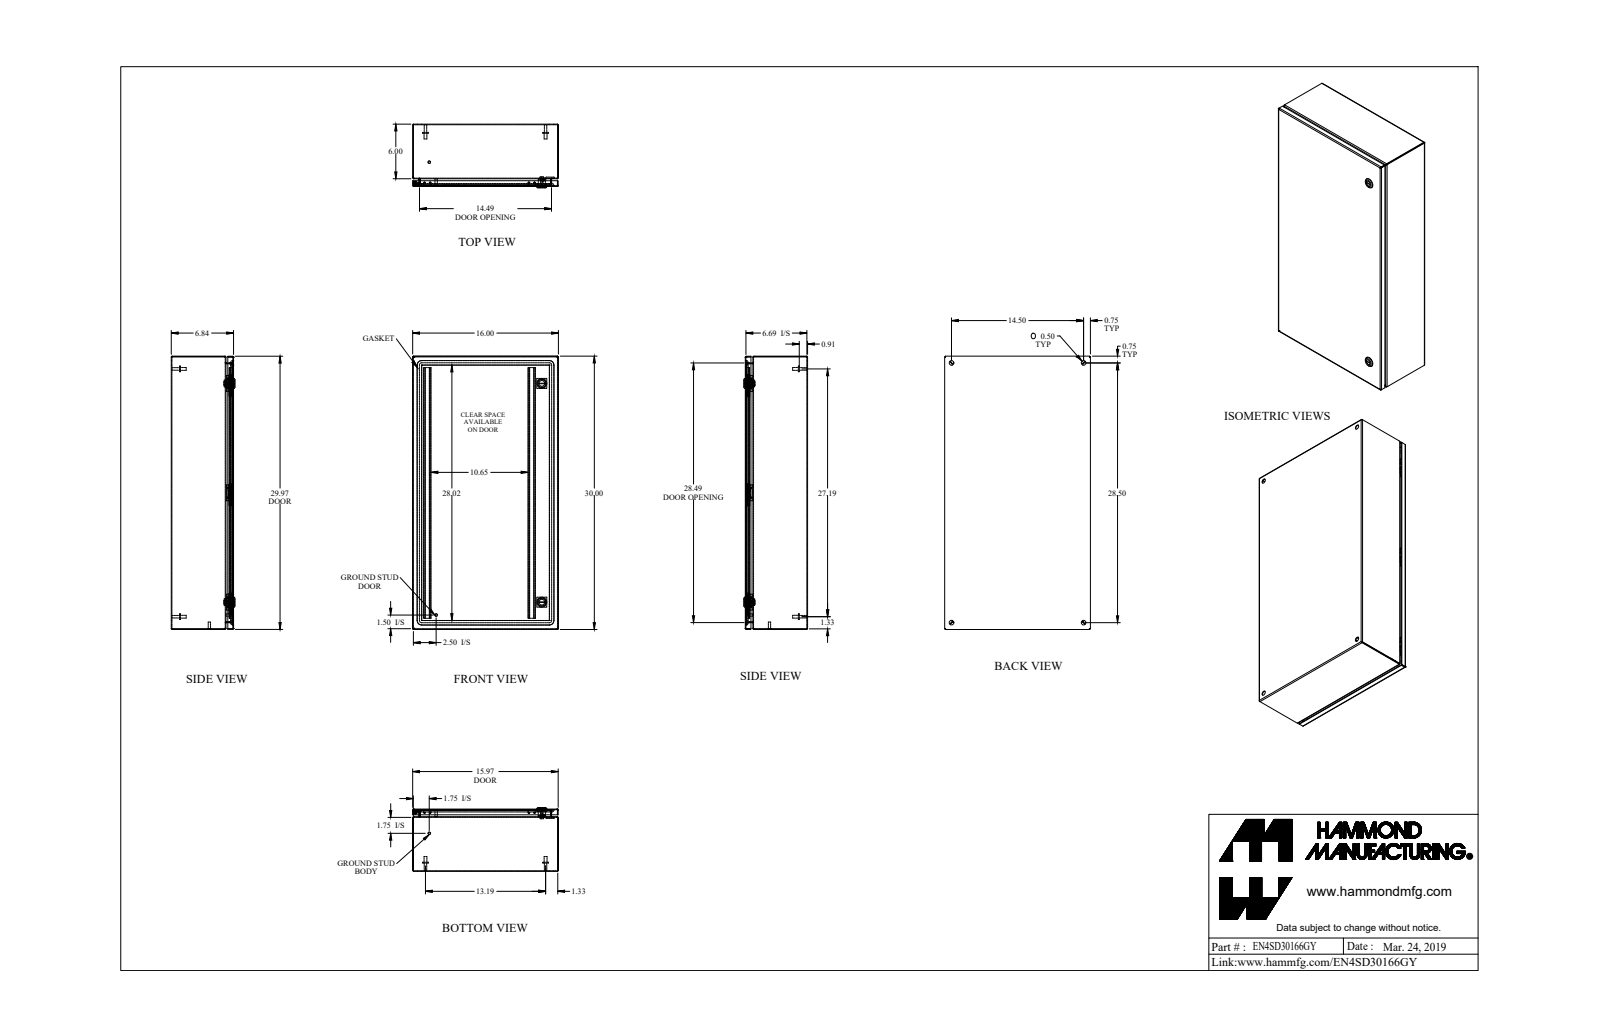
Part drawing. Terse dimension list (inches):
name: EN4SD30166GY_Default
written by: SolidWorks 2019 (CONFIG_CONTROL_DESIGN)
unit: in
bodies: 31 solids, 885 faces (422 planar, 295 cylindrical, 168 other)
size: 30 × 16 × 6.997
volume: 134.9 in³; area: 3 806 in²
holes: 4× ⌀0.5, 2× ⌀0.232, 2× ⌀0.625, 2× ⌀0.785, 1× ⌀0.172, 1× ⌀0.24, 1× ⌀0.242
bosses: 4× ⌀0.625, 4× ⌀0.313, 4× ⌀0.27, 2× ⌀1.1, 2× ⌀0.525, 2× ⌀0.281, 2× ⌀0.25, 1× ⌀0.455
rounds: 20× R0.036, 20× R0.108, 12× R0.043, 12× R0.081, 12× R0.382, 8× R19.003, 6× R0.006, 6× R0.062
face distances: 0.072, 6.765, 6.693, 6.837, 15.928, 29.928, 15.856, 16, 0.837, 5.928
hole spacings: 13.615, 14.5, 28.5, 31.976, 2.493, 2.494, 23.999, 26.271
